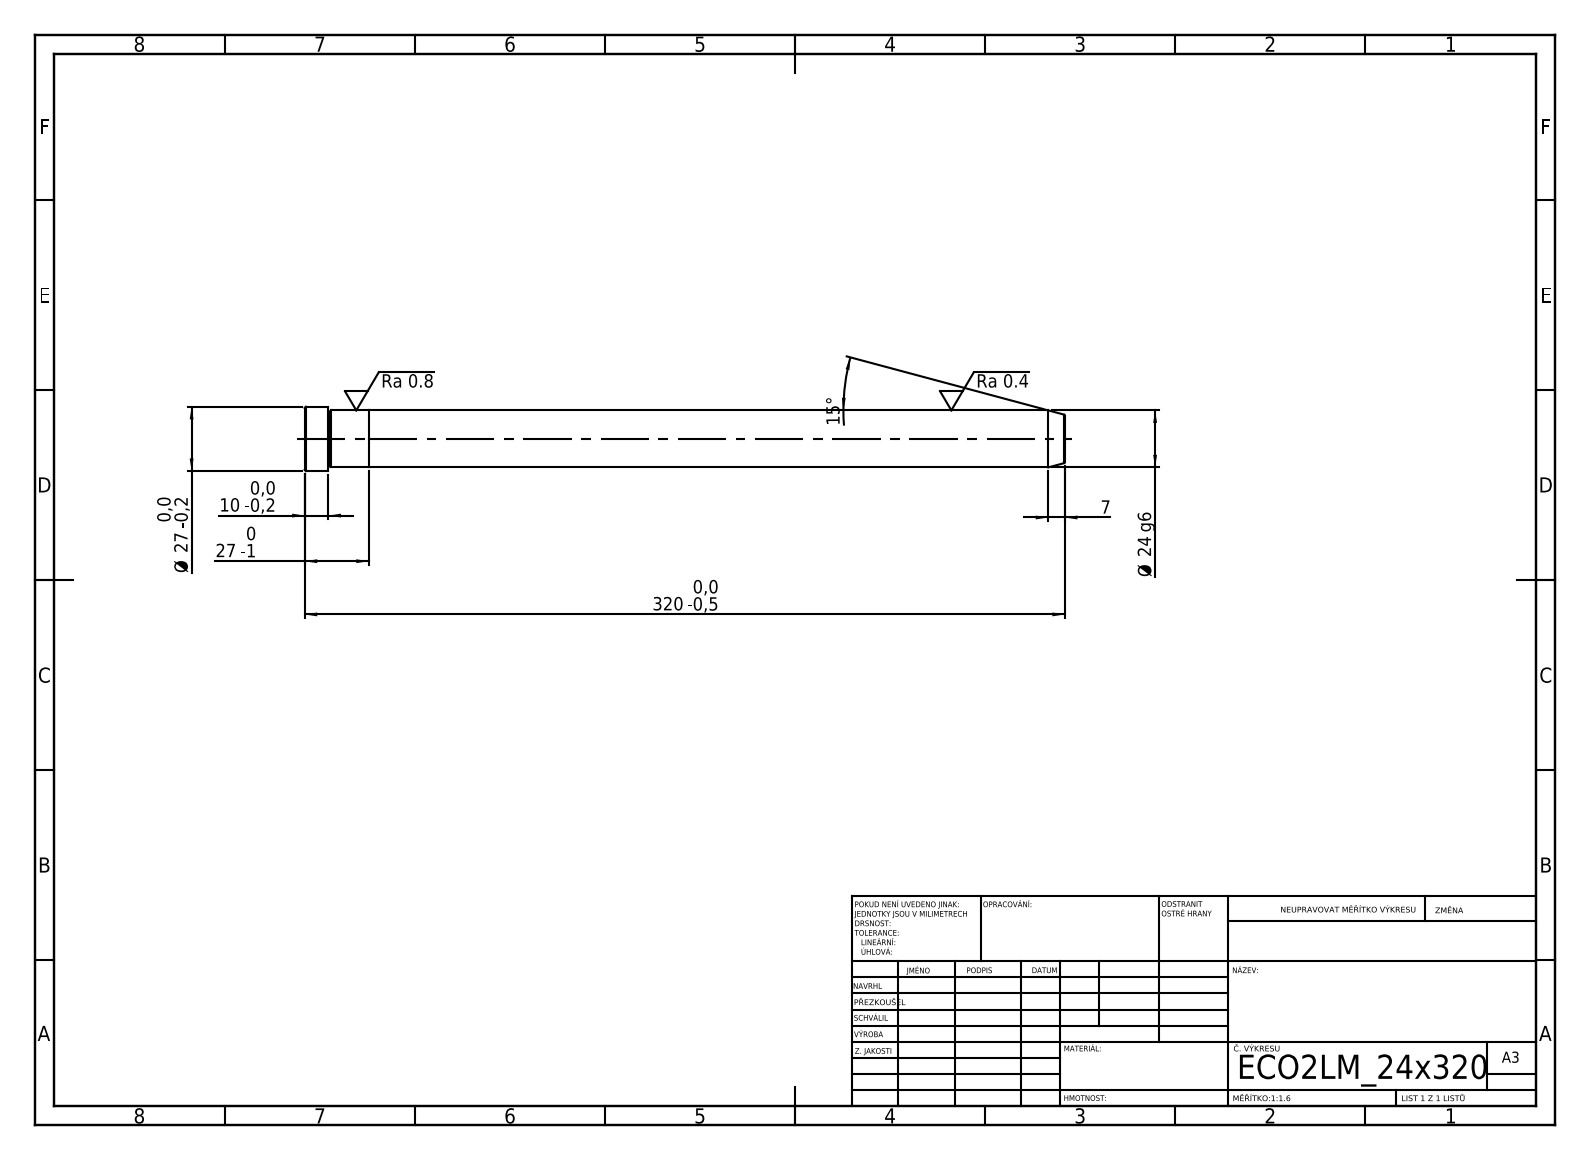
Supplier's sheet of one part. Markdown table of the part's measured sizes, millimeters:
| quantity | value |
| --- | --- |
| STEP written by | SolidWorks 2019 (CONFIG_CONTROL_DESIGN) |
| units | millimeters |
| bodies | 2 solids, 21 faces (5 planar, 6 cylindrical, 10 other) |
| overall size | 320 × 27 × 27 |
| volume | 145 456 mm³ |
| surface area | 26 125 mm² |
| round bosses / shafts (diameter × count) | 27 × 1, 24 × 1 |
| main face-to-face distances | 27, 293, 320, 310, 17, 10 |
